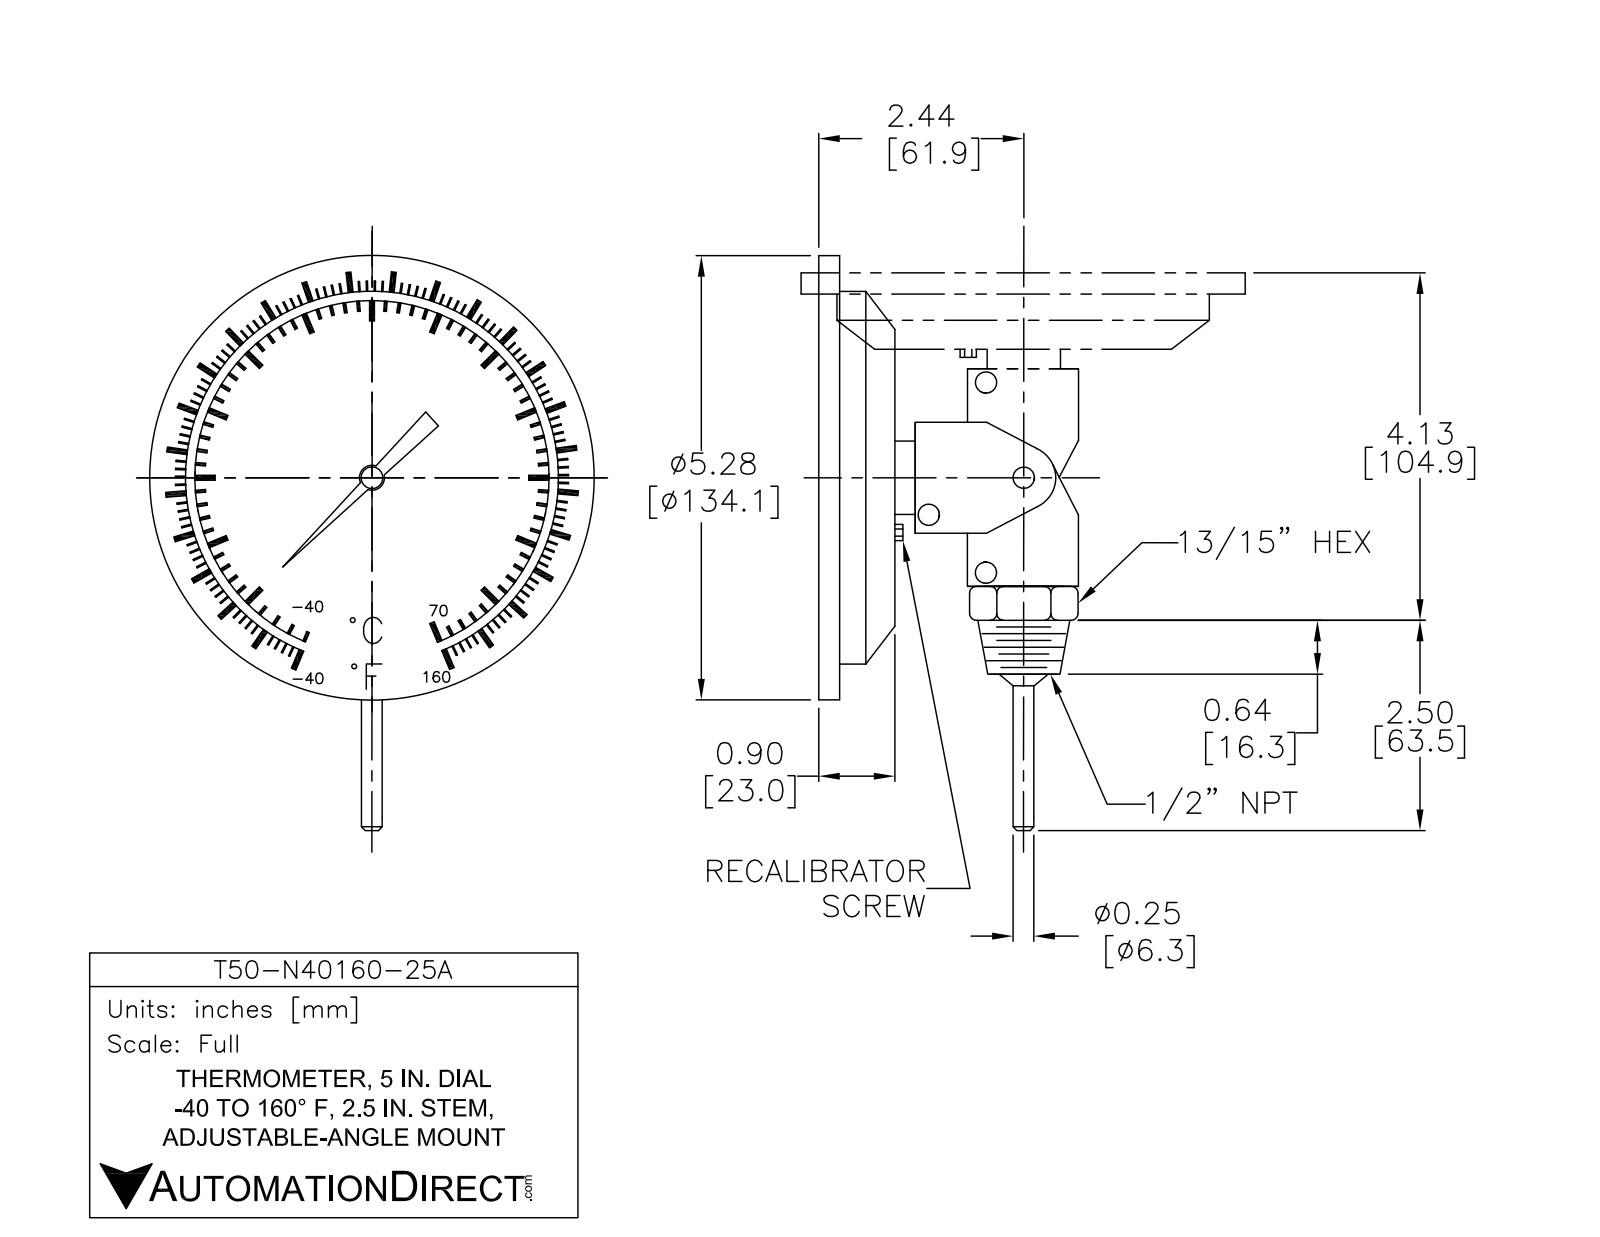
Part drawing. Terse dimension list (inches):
name: T50-N40160-25A
written by: SolidWorks 2021 (AUTOMOTIVE_DESIGN)
unit: in
bodies: 1 solid, 513 faces (319 planar, 45 cylindrical, 149 other)
size: 6.46 × 5.28 × 5.28
volume: 10.06 in³; area: 95.62 in²
holes: 1× ⌀3.424, 1× ⌀3.7, 1× ⌀4.76, 1× ⌀4.836
bosses: 4× ⌀0.305, 2× ⌀0.145, 1× ⌀5.28, 1× ⌀4.97, 1× ⌀3.73, 1× ⌀3.454, 1× ⌀0.85, 1× ⌀0.821
rounds: 10× R0.06, 4× R0.04, 1× R0.17, 1× R0.336, 1× R0.336, 1× R0.342, 1× R0.4
face distances: 0.353, 0.074, 0.055, 0.427, 1.19, 0.815, 0.462, 0.388, 1.245, 2.435
